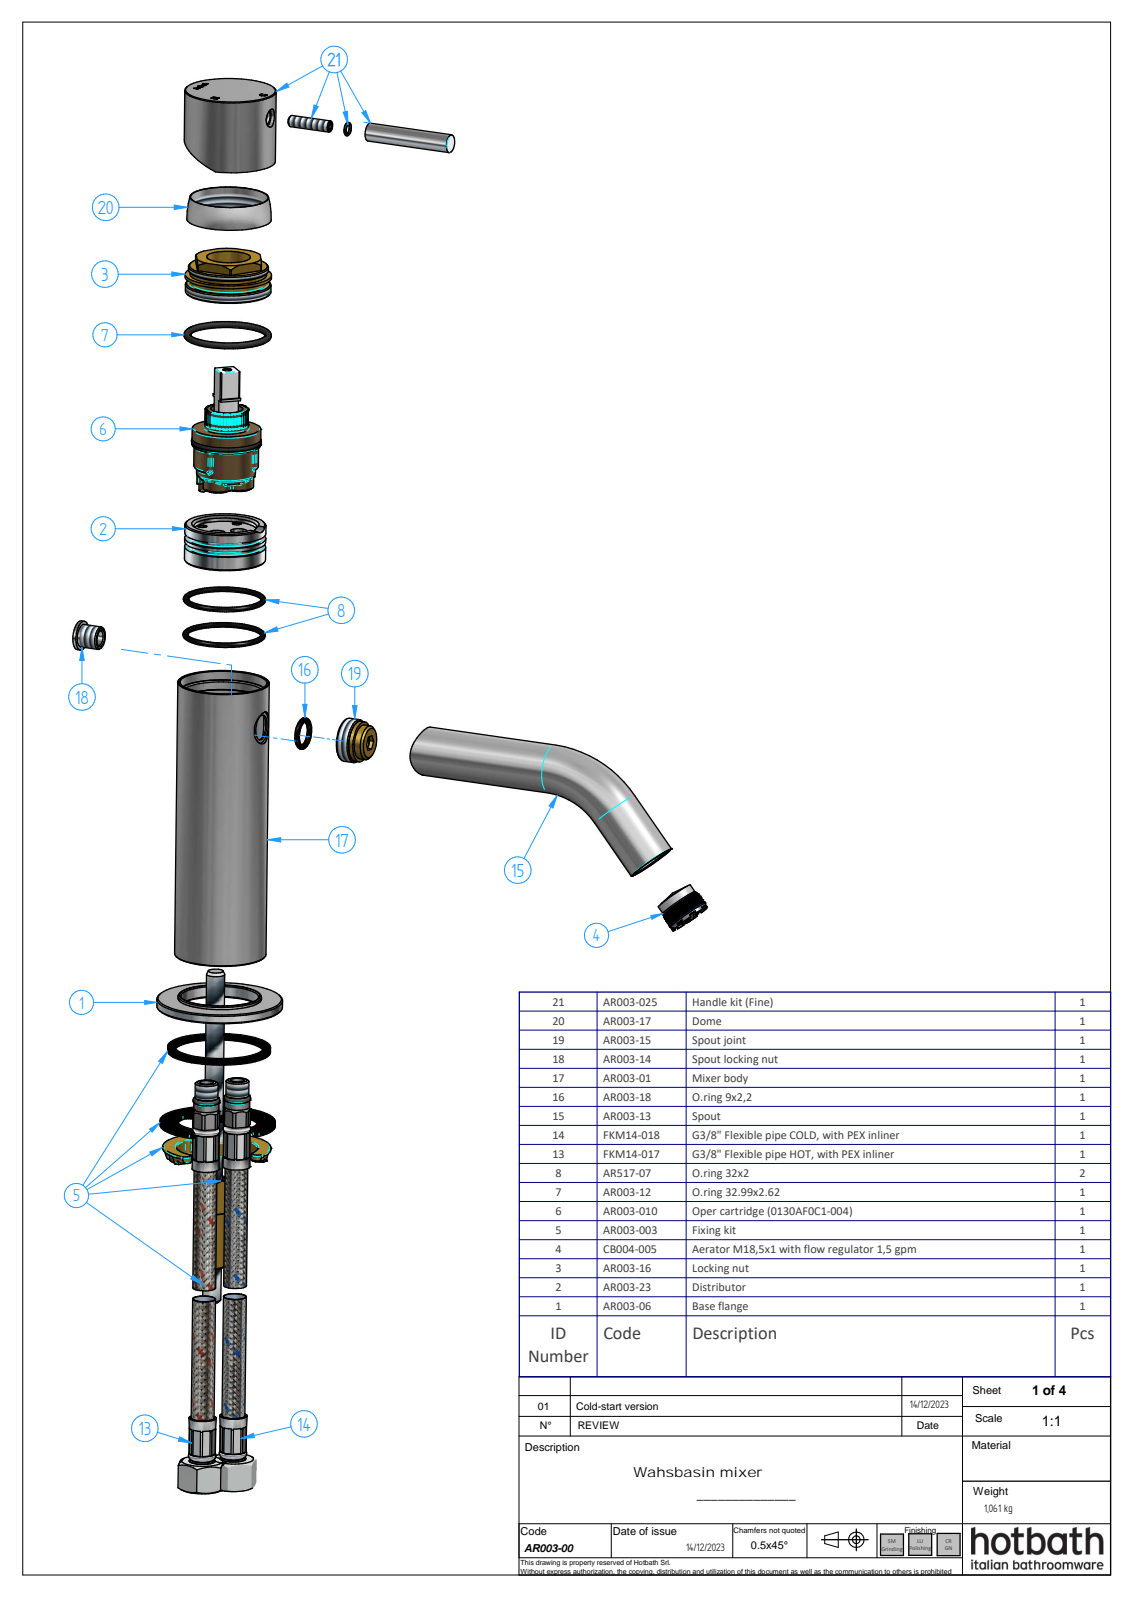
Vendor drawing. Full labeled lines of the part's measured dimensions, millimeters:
Part name (STEP PRODUCT): AR003-00 rel1; AR003-06; AR003-17; CB004-005 (+5 more)
STEP written by: Solid Edge (AUTOMOTIVE_DESIGN)
Units: millimetres
Bodies: 7 solids, 982 faces (634 planar, 300 cylindrical, 48 other)
Overall size (bounding box): 165.74 × 161 × 55
Volume: 87 605 mm³ · Surface area: 63 892 mm²
Round holes (diameter × count): ⌀0.75 ×116, ⌀15.3 ×2, ⌀4.13 ×1, ⌀8 ×1, ⌀9.5 ×1, ⌀11 ×1, ⌀13.5 ×1, ⌀13.8 ×1, ⌀14.1 ×1, ⌀15 ×1, ⌀17 ×1, ⌀17.42 ×1
Round bosses / shafts (diameter × count): ⌀21.3 ×2, ⌀55 ×1, ⌀40 ×1, ⌀39 ×1, ⌀36.5 ×1, ⌀18.5 ×1, ⌀18.4 ×1, ⌀17.4 ×1
Partial cylindrical surfaces — rounded edges, fillets, slot ends (radius × count): R0.1 ×4, R1.5 ×4, R0.24 ×2, R0.39 ×2, R0.44 ×2, R0.69 ×2, R0.62 ×1, R0.62 ×1
Main face-to-face distances: 157, 16, 141, 4, 145, 161, 2.2, 1.8, 142.8, 158.8
Hole centre spacings: 3.07, 3.08, 0.89, 1.17, 2.08, 2.8, 3.04, 3.83
